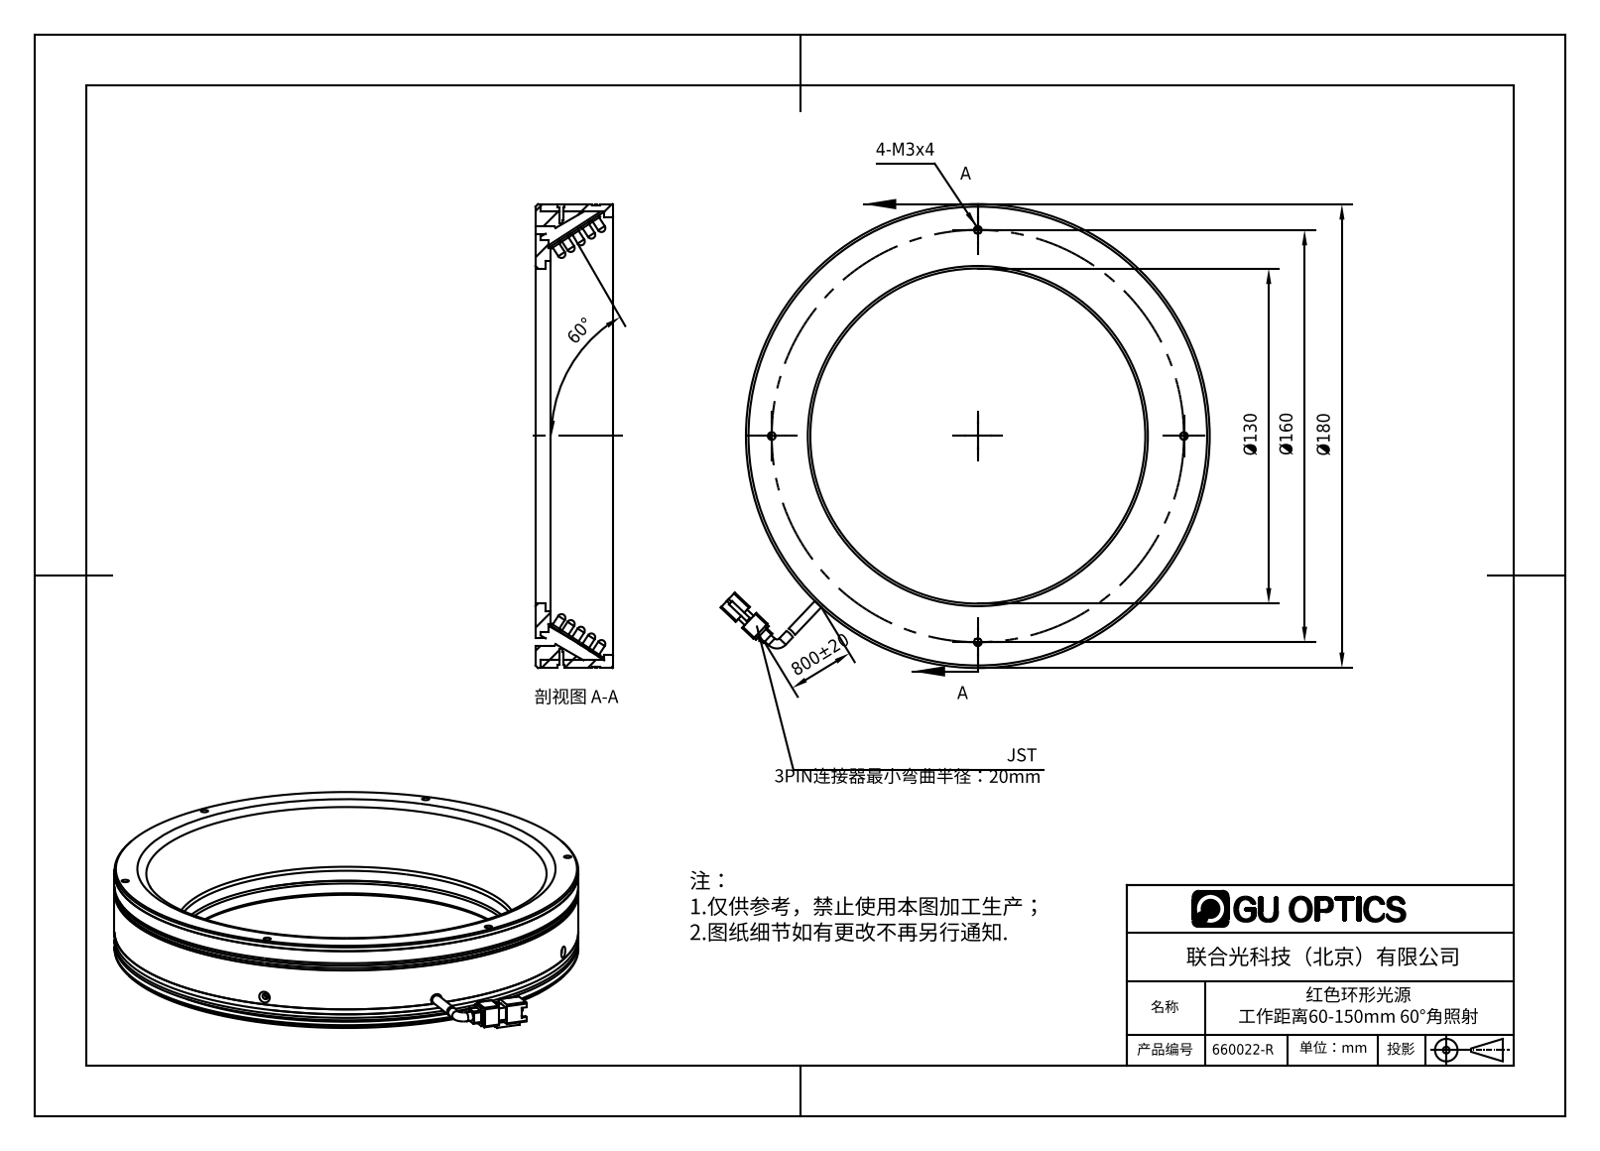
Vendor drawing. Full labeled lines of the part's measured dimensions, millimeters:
Part name (STEP PRODUCT): 660022-R
STEP written by: SolidWorks 2016 (AUTOMOTIVE_DESIGN)
Units: millimetres
Bodies: 506 solids, 8844 faces (6099 planar, 2169 cylindrical, 576 other)
Overall size (bounding box): 189.81 × 180 × 34
Volume: 204 941 mm³ · Surface area: 199 276 mm²
Round holes (diameter × count): ⌀1.6 ×8, ⌀1.25 ×6, ⌀1.5 ×6, ⌀2.8 ×6, ⌀3.5 ×5, ⌀2.5 ×4, ⌀3 ×4, ⌀2.4 ×2, ⌀130 ×1, ⌀131 ×1, ⌀136 ×1, ⌀170 ×1
Round bosses / shafts (diameter × count): ⌀3.8 ×500, ⌀3 ×500, ⌀3.5 ×2, ⌀180 ×1, ⌀179 ×1, ⌀174 ×1, ⌀172 ×1, ⌀151.08 ×1
Partial cylindrical surfaces — rounded edges, fillets, slot ends (radius × count): R0.5 ×12, R1 ×4, R1.75 ×1, R6 ×1
Main face-to-face distances: 2, 1, 3.5, 4.5, 32, 26, 1.5, 2.5, 30.5, 3
Hole centre spacings: 87, 150.69, 168.07, 43.75, 45.04, 83.72, 118.19, 144.67
